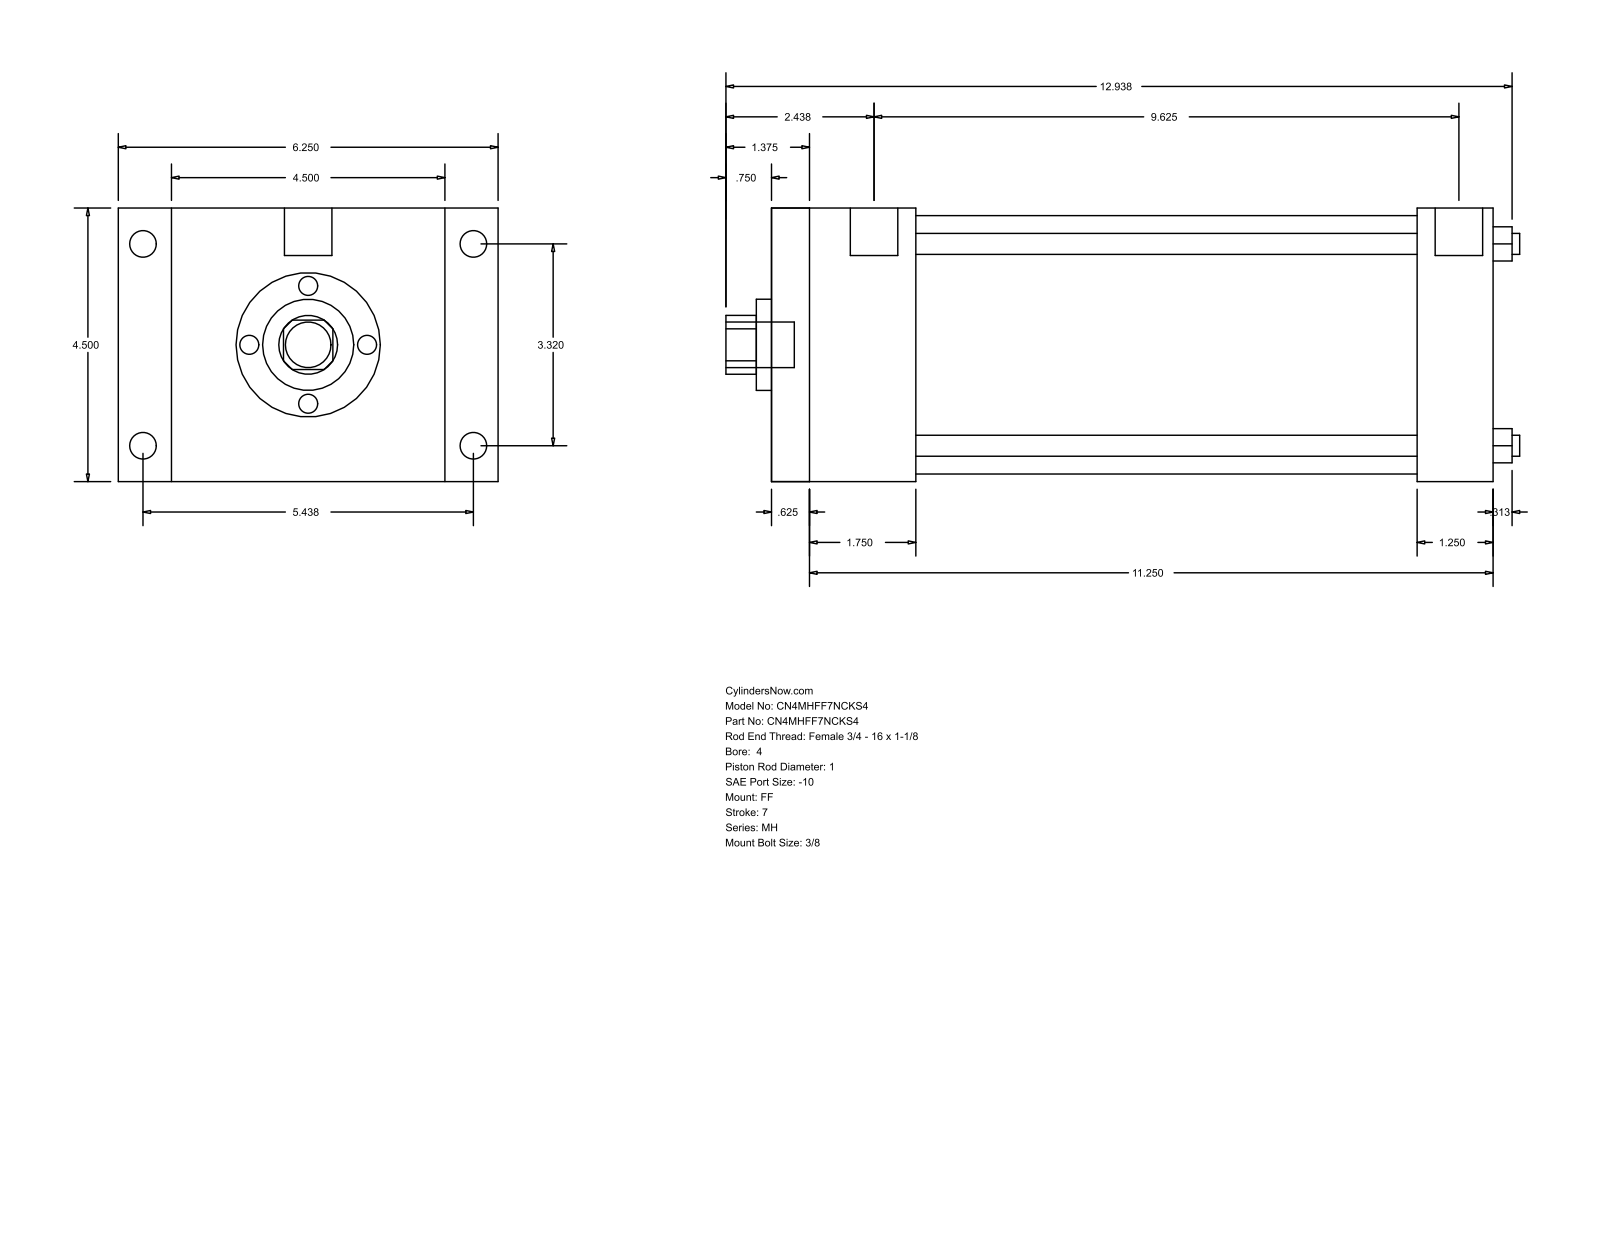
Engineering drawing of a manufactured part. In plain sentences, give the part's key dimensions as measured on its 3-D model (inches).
The part is named "MH_FF__0400_1". Its 3-D file was written by "GSSL Pune (CONFIG_CONTROL_DESIGN)". It is 0 solids with 92 faces: 64 planar, 28 cylindrical and 0 other. Overall it measures 13.063 by 6.25 by 4.5 inches. Round holes: 4 of diameter 0.345, 1 of diameter 1, 1 of diameter 1.5, 1 of diameter 4.25. Round bosses or shafts: 4 of diameter 0.438, 4 of diameter 0.344, 2 of diameter 0.781, 1 of diameter 0.75. Partial cylindrical surfaces (rounded edges, fillets, slot ends): 1 of radius 0.484. The main face-to-face distances are 4.5, 11.875, 0.625, 11.25, 2.375, 1.75, 9.5, 10.625, 10, 8.25. The hole center spacings are 2.347, 3.32, 4.695.
